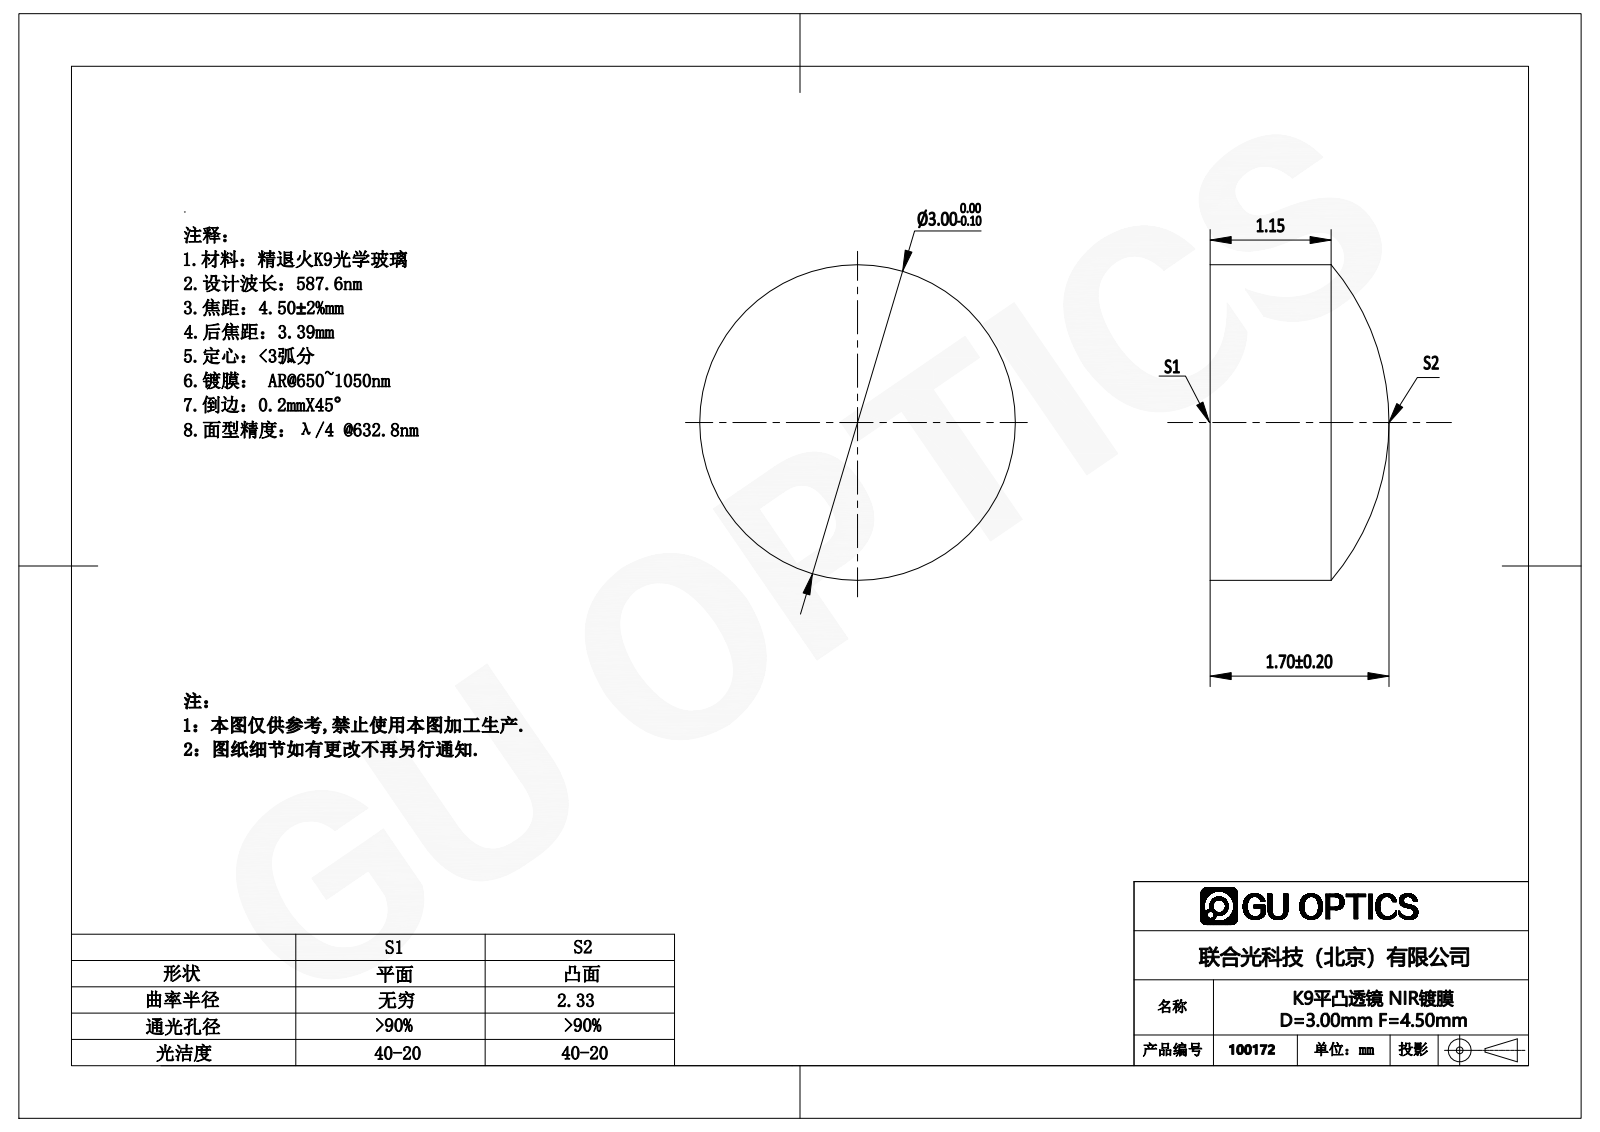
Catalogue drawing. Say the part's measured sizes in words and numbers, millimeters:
The part is named "100172". Its 3-D file was written by "SolidWorks 2016 (AUTOMOTIVE_DESIGN)". It is 1 solid with 5 faces: 1 planar, 2 cylindrical and 2 other. Overall it measures 3 by 3 by 1.7 millimeters. Its volume is 10 cubic millimeters and its surface area 26 square millimeters. Round bosses or shafts: 1 of diameter 3.
